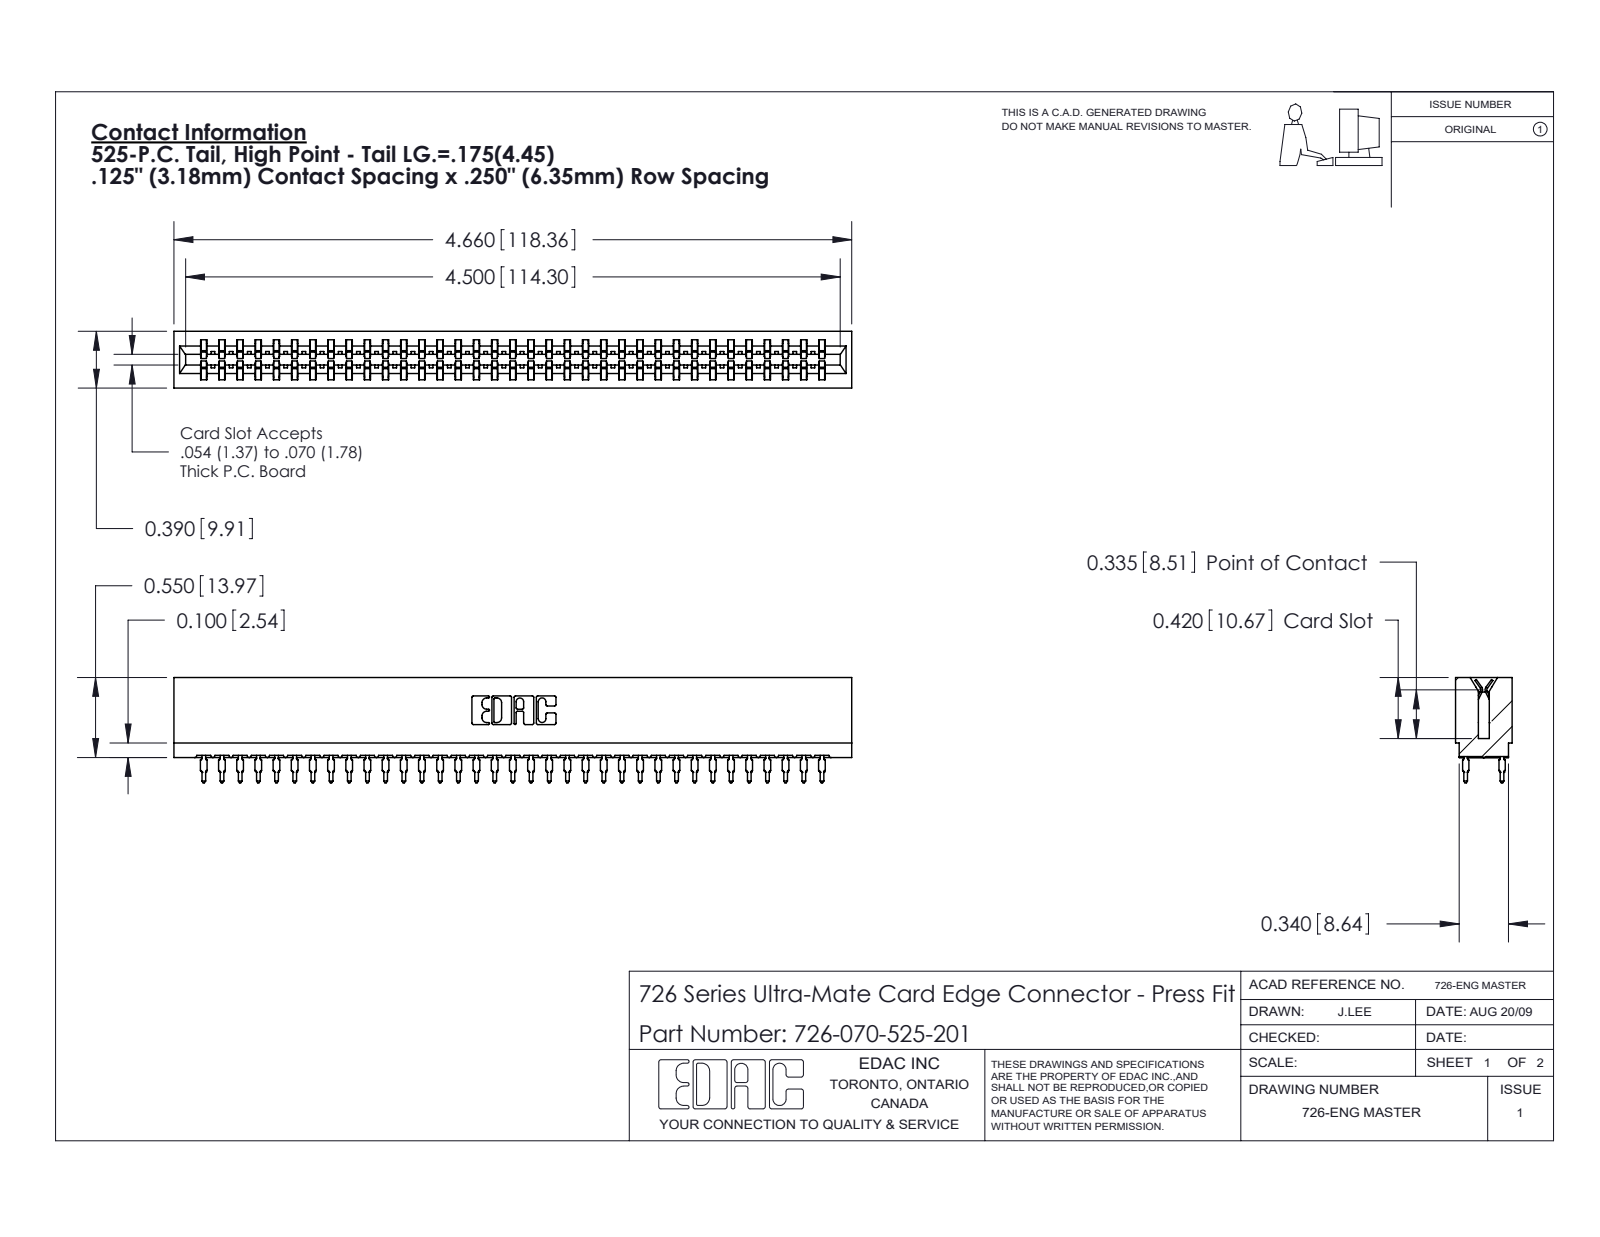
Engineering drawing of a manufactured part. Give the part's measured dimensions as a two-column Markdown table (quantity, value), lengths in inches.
| quantity | value |
| --- | --- |
| part name | 726 Part_.515 Slot Depth - 01; 746-292-001_525; 726-070-525-201 |
| STEP written by | SolidWorks 2020 (CONFIG_CONTROL_DESIGN) |
| units | inches |
| bodies | 71 solids, 6362 faces (3275 planar, 1267 cylindrical, 1820 other) |
| overall size | 4.66 × 0.724 × 0.39 |
| volume | 0.665 in³ |
| surface area | 27.7 in² |
| partial cylindrical surfaces (radius × count) | 0.021 × 140, 0.015 × 36, 0.01 × 22, 0.005 × 8, 0.011 × 8, 0.007 × 6, 0.031 × 6, 0.026 × 3 |
| main face-to-face distances | 0.057, 0.333, 0.39, 0.25, 0.025, 0.307, 0.275, 0.5, 0.083, 0.365 |
